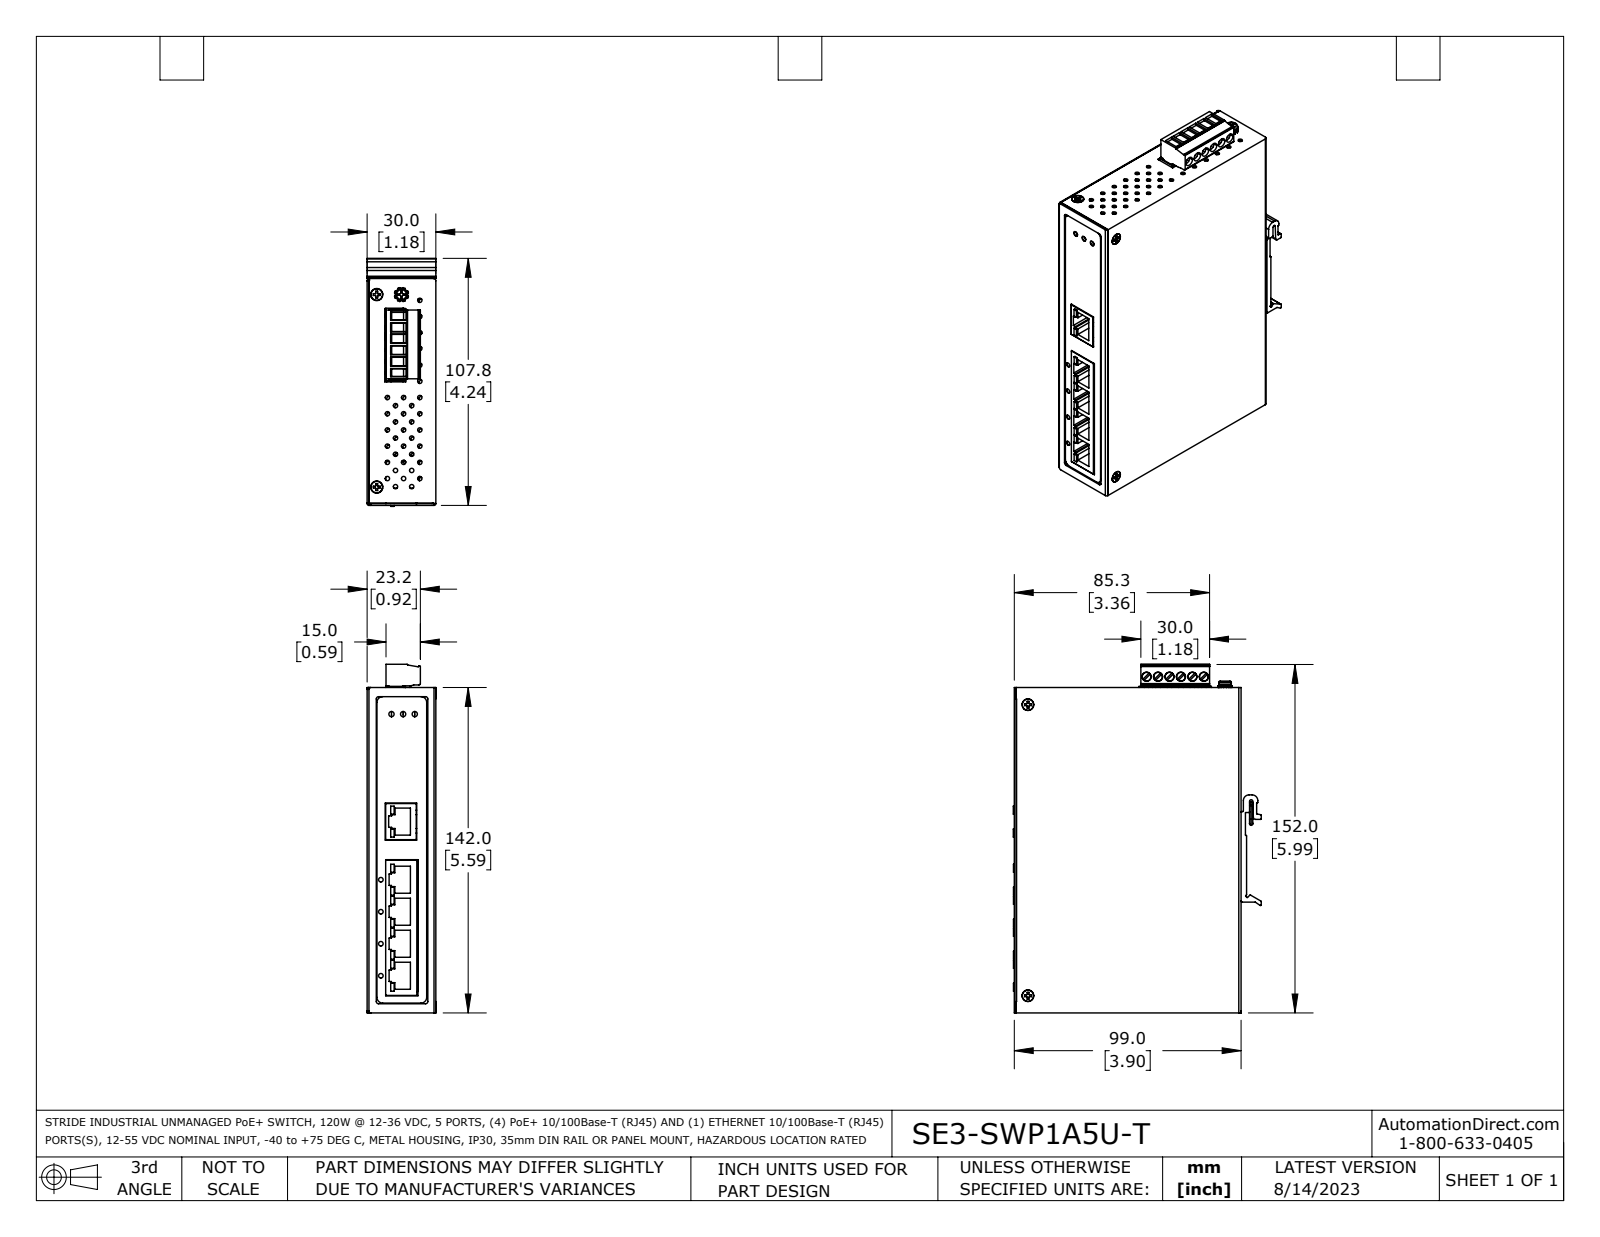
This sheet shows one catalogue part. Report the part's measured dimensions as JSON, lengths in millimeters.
{"part_name": "LEONTON_EG2-0800_3D sr1 solid but 16 bad faces1 extTB1ac coord pre CASE MOD for PT2-0500 1aCd cmb1Cc CASE ONLY mm coord fxt", "step_written_by": "SolidWorks 2021 (AUTOMOTIVE_DESIGN)", "units": "millimeters", "bodies": {"solids": 37, "faces": 2088, "planar": 1040, "cylindrical": 788, "other": 260}, "overall_size": [152.1, 108.2, 30], "volume_mm3": 64270, "surface_area_mm2": 107500, "round_holes": [[1.9, 111], [4, 9], [2.5, 8], [2, 4], [2.5, 4], [2.3, 3], [3, 3], [2.4, 2], [2.4, 2], [5, 2], [5.3, 2], [1.5, 1]], "round_bosses_or_shafts": [[3, 13], [5, 10], [4.1, 8], [3.8, 6], [1.4, 6], [0.9, 6], [4.2, 4], [4, 4]], "partial_cylinders_radius": [[0.3, 52], [0.1, 47], [0.2, 37], [1, 17], [0.3, 14], [0.5, 9], [0.8, 8], [2.5, 7]], "face_to_face_distances": [0.8, 1, 29.2, 28.2, 29, 30, 141.2, 0.5, 7.3, 20.9], "hole_center_spacings": [11.2, 7.1, 5, 10, 14.1, 15.8, 15, 29.2]}
